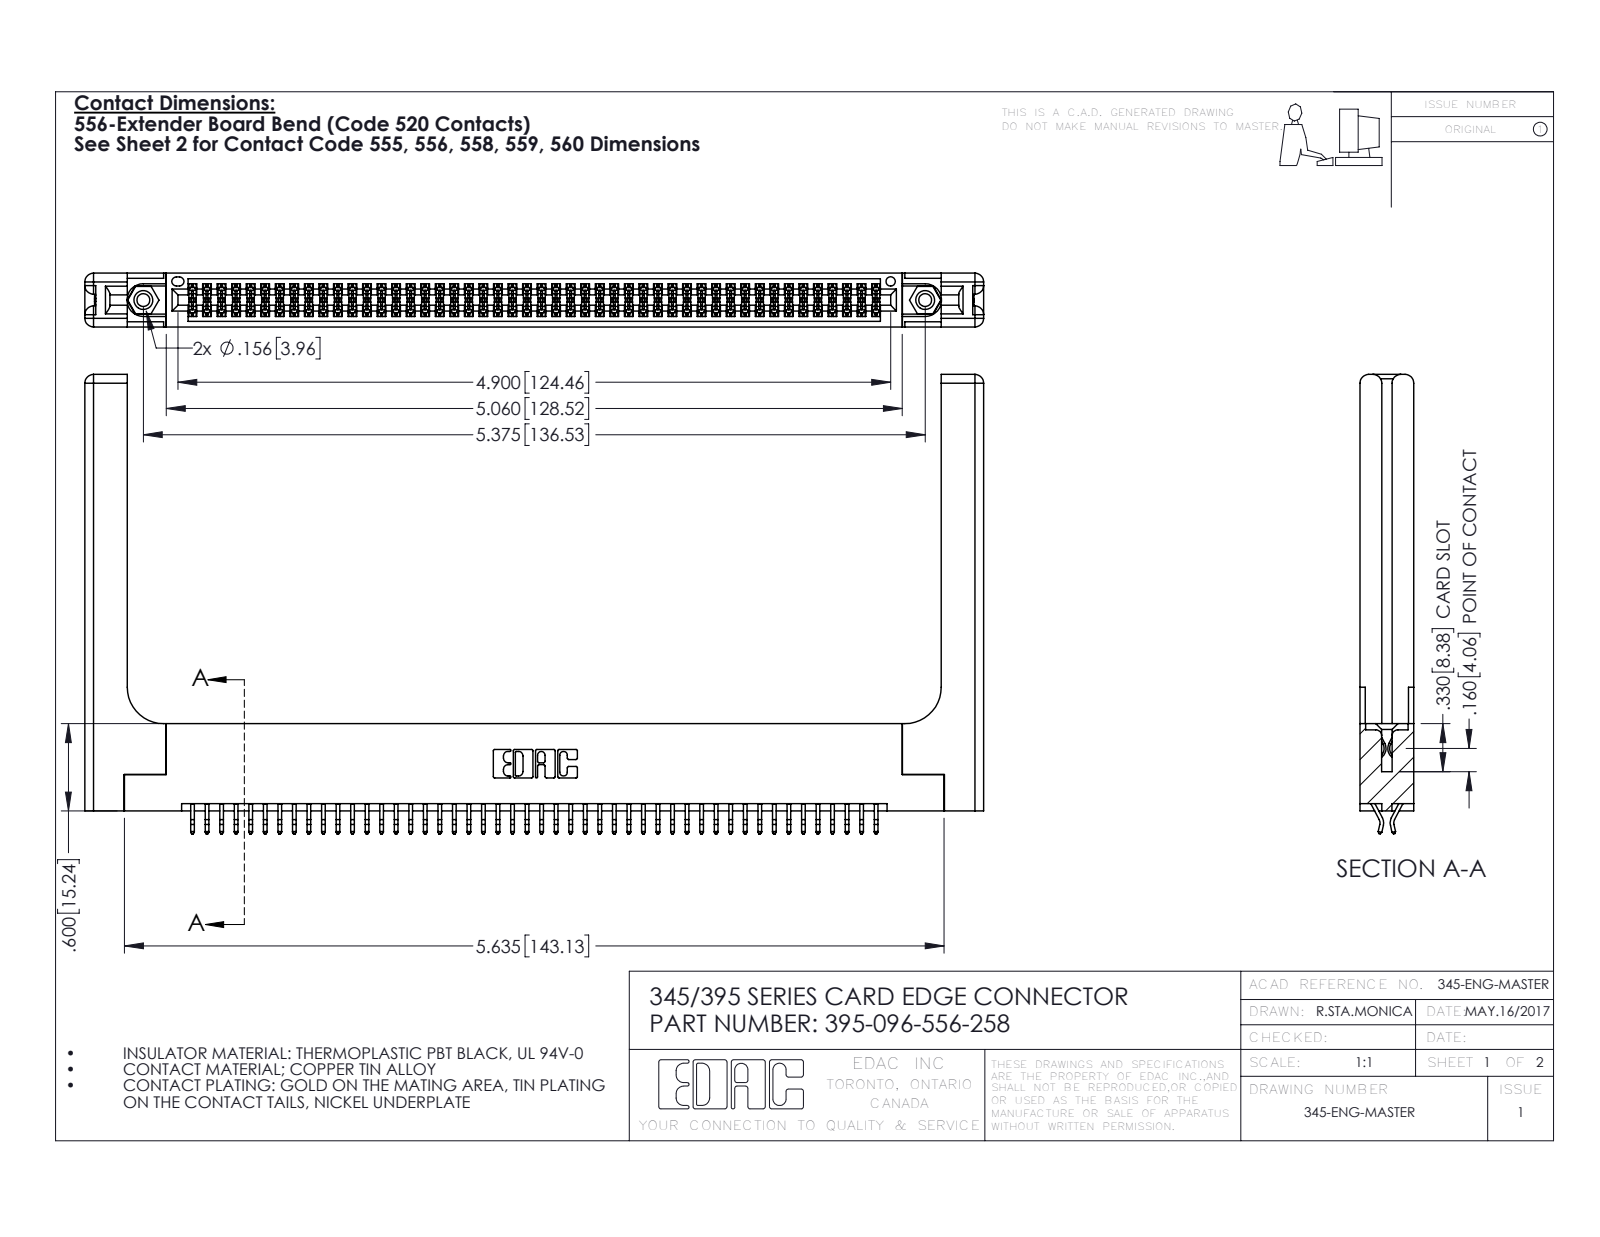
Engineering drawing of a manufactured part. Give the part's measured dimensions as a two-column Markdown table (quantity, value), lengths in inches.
| quantity | value |
| --- | --- |
| part name | 345-292-001_556 Tail; 345-220-058_345-220-058; 395-096-556-258; 345-250-001_345-250-001-102 (+1 more) |
| STEP written by | SolidWorks 2016 (CONFIG_CONTROL_DESIGN) |
| units | inches |
| bodies | 101 solids, 5758 faces (3780 planar, 1918 cylindrical, 60 other) |
| overall size | 6.179 × 3.157 × 0.37 |
| volume | 1.451 in³ |
| surface area | 42.94 in² |
| round holes (diameter × count) | 0.089 × 2, 0.125 × 2, 0.156 × 2, 0.064 × 1 |
| round bosses / shafts (diameter × count) | 0.155 × 2 |
| partial cylindrical surfaces (radius × count) | 0.006 × 144, 0.01 × 22, 0.06 × 16, 0.007 × 6, 0.031 × 6, 0.026 × 3, 0.01 × 2, 0.014 × 2 |
| main face-to-face distances | 0.072, 0.37, 0.298, 0.2, 0.025, 0.098, 0.272, 0.225, 0.148, 0.15 |
| hole center spacings | 0.27, 5.139, 5.375 |
